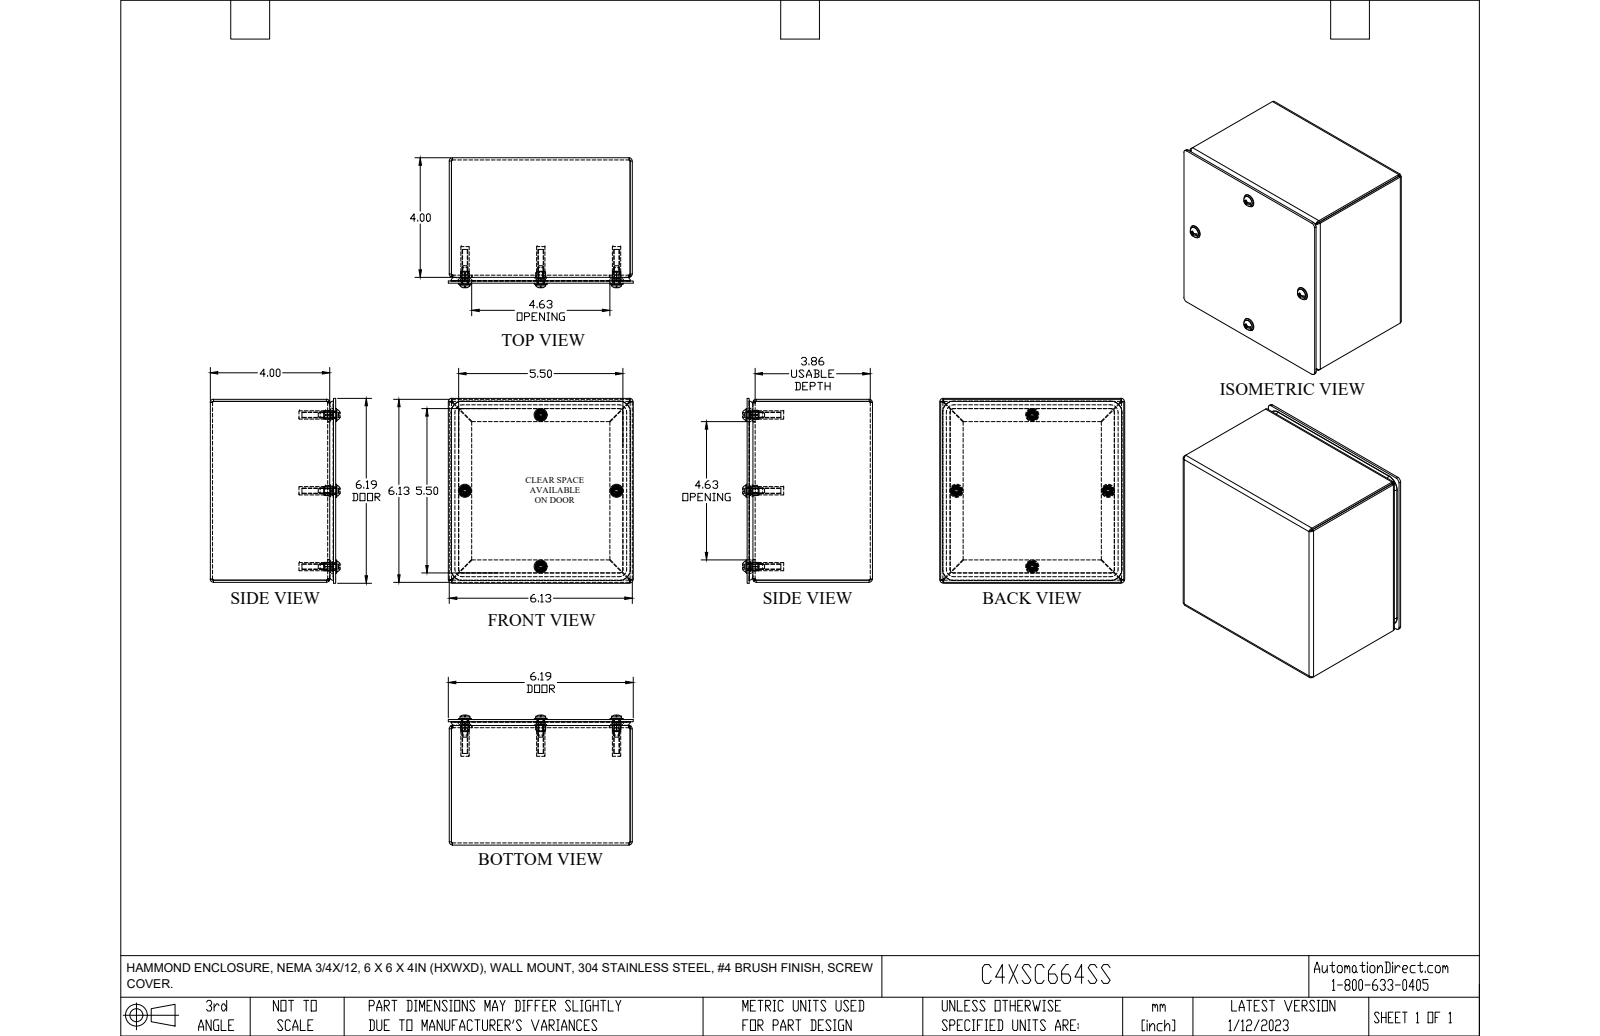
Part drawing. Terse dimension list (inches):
name: C3SC664GY
written by: SolidWorks 2021 (AUTOMOTIVE_DESIGN)
unit: in
bodies: 15 solids, 461 faces (289 planar, 92 cylindrical, 80 other)
size: 6.188 × 6.188 × 4.347
volume: 13.73 in³; area: 408.2 in²
holes: 4× ⌀0.159, 4× ⌀0.16, 4× ⌀0.25
bosses: 4× ⌀0.44, 4× ⌀0.39, 4× ⌀0.24, 4× ⌀0.19, 4× ⌀0.148, 3× ⌀0.275, 1× ⌀0.275
rounds: 8× R0.04, 8× R0.11, 8× R0.125, 4× R0.126, 4× R0.16, 4× R0.374
face distances: 0.07, 6.055, 6.125, 5.985, 0.072, 4.127, 4.197, 4.055, 4.125, 3.93
hole spacings: 3.589, 5.075
